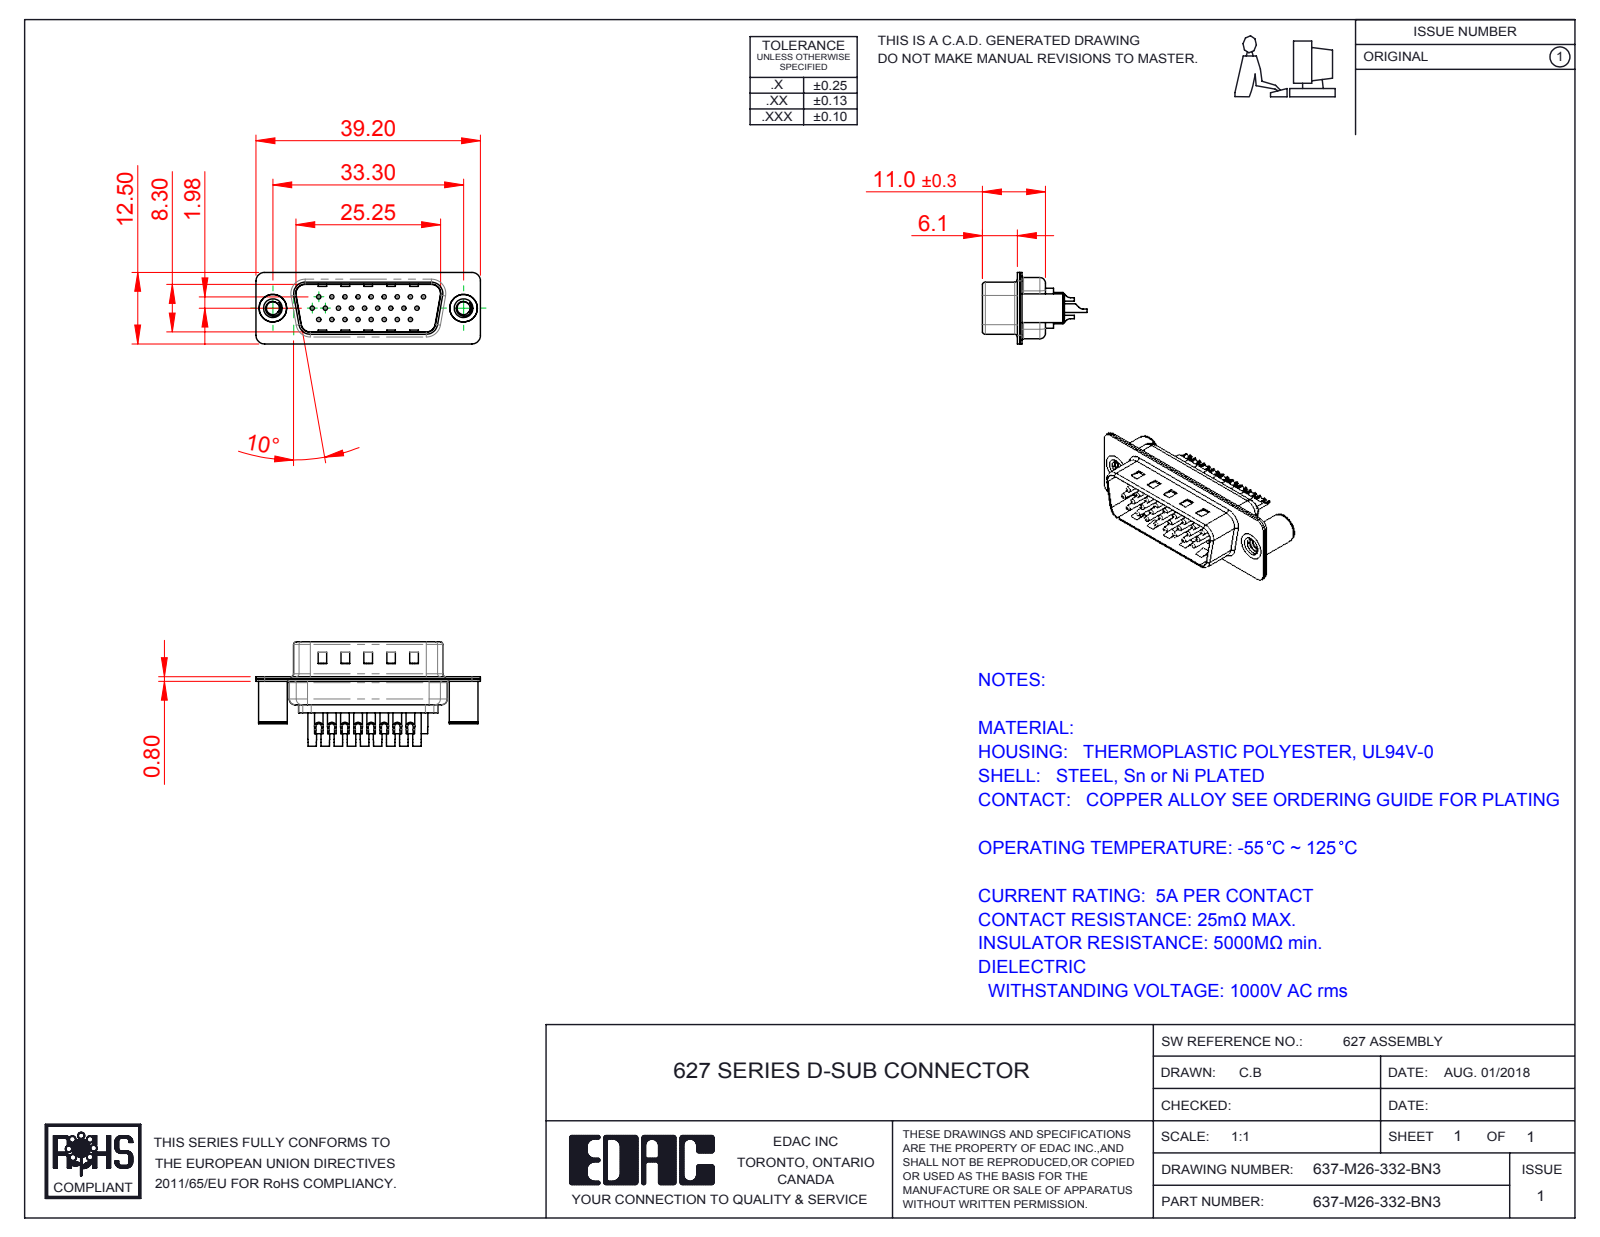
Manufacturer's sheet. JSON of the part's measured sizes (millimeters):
{"part_name": "637M Housing_26 Contacts; 637M Contact Row 2_32; 637M Contact Row 1_32; 637M 4-40 Threaded Board Spacer (+4 more)", "step_written_by": "SolidWorks 2016 (CONFIG_CONTROL_DESIGN)", "units": "millimeters", "bodies": {"solids": 31, "faces": 1336, "planar": 373, "cylindrical": 573, "other": 390}, "overall_size": [39.2, 18.25, 12.5], "volume_mm3": 2118, "surface_area_mm2": 6331, "round_holes": [[0.75, 26], [1, 26], [1.6, 26], [2, 26], [2.26, 2], [3.26, 2], [4, 2], [4.8, 2]], "round_bosses_or_shafts": [[1.5, 26], [5, 2], [4.9, 2]], "partial_cylinders_radius": [[1.5, 16], [2, 12], [0.5, 8], [1.6, 8], [1, 7], [0.25, 4], [0.6, 4], [0.65, 4]], "face_to_face_distances": [0.4, 0.8, 9.5, 9.1, 8.7, 9.9, 0.75, 0.35, 1.2, 1.9], "hole_center_spacings": [3.96, 2.28, 4.57, 6.05, 2.29, 8.24, 6.86, 10.48]}
